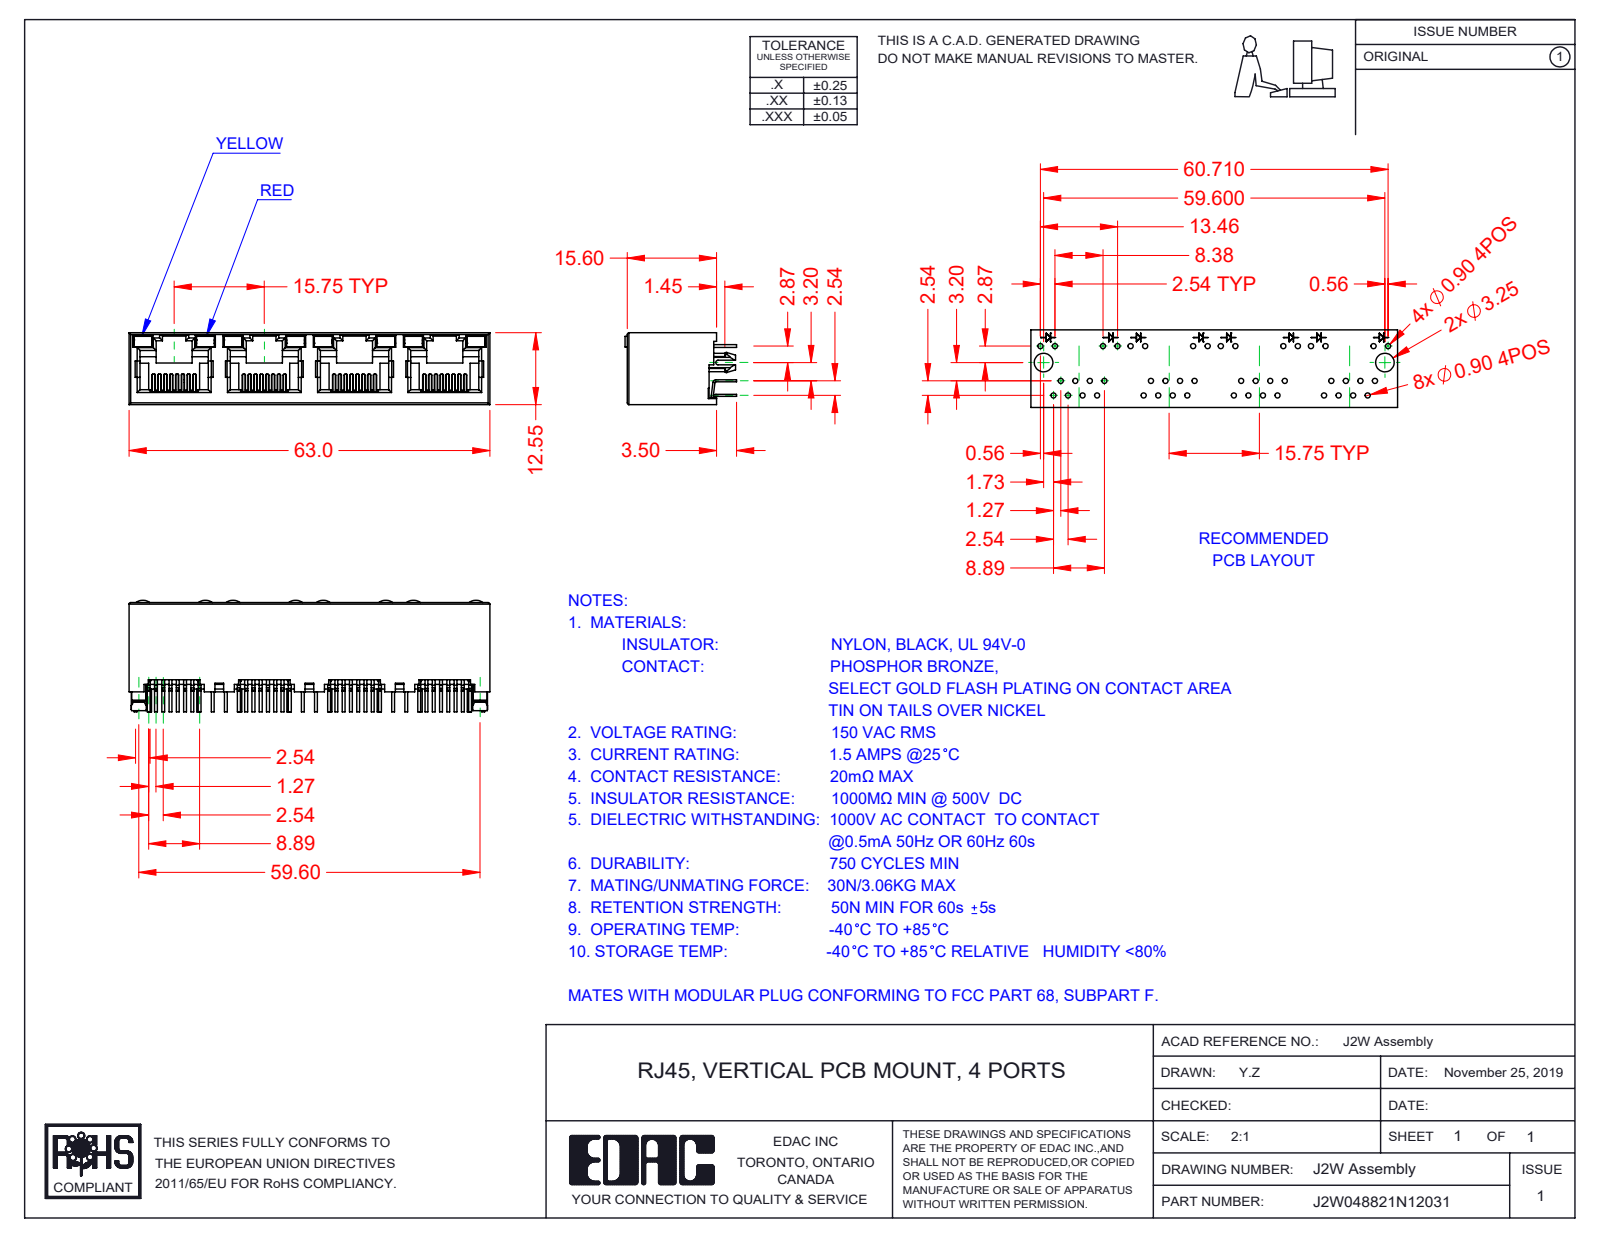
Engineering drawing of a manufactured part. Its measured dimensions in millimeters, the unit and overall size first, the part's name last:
Units: millimetres
Overall size (bounding box): 63 × 19.5 × 12.55
Partial cylindrical surfaces — rounded edges, fillets, slot ends (radius × count): R0.15 ×64, R0.2 ×29, R0.5 ×28, R0.3 ×14, R0.45 ×8, R2 ×8, R0.25 ×2, R1.5 ×2
Main face-to-face distances: 12.55, 11.9, 0.65, 15.75, 0.36, 1.5, 0.78, 0.6, 11.3, 31.5
Volume: 5 335 mm³ · Surface area: 13 144 mm²
Bodies: 45 solids, 3135 faces (2600 planar, 477 cylindrical, 58 other)
Part name (STEP PRODUCT): 2W LED LH_1-Yellow; J2W048821N12031; 2W Insulator; 2W Contact Lock (+2 more)
STEP written by: SolidWorks 2020 (CONFIG_CONTROL_DESIGN)
